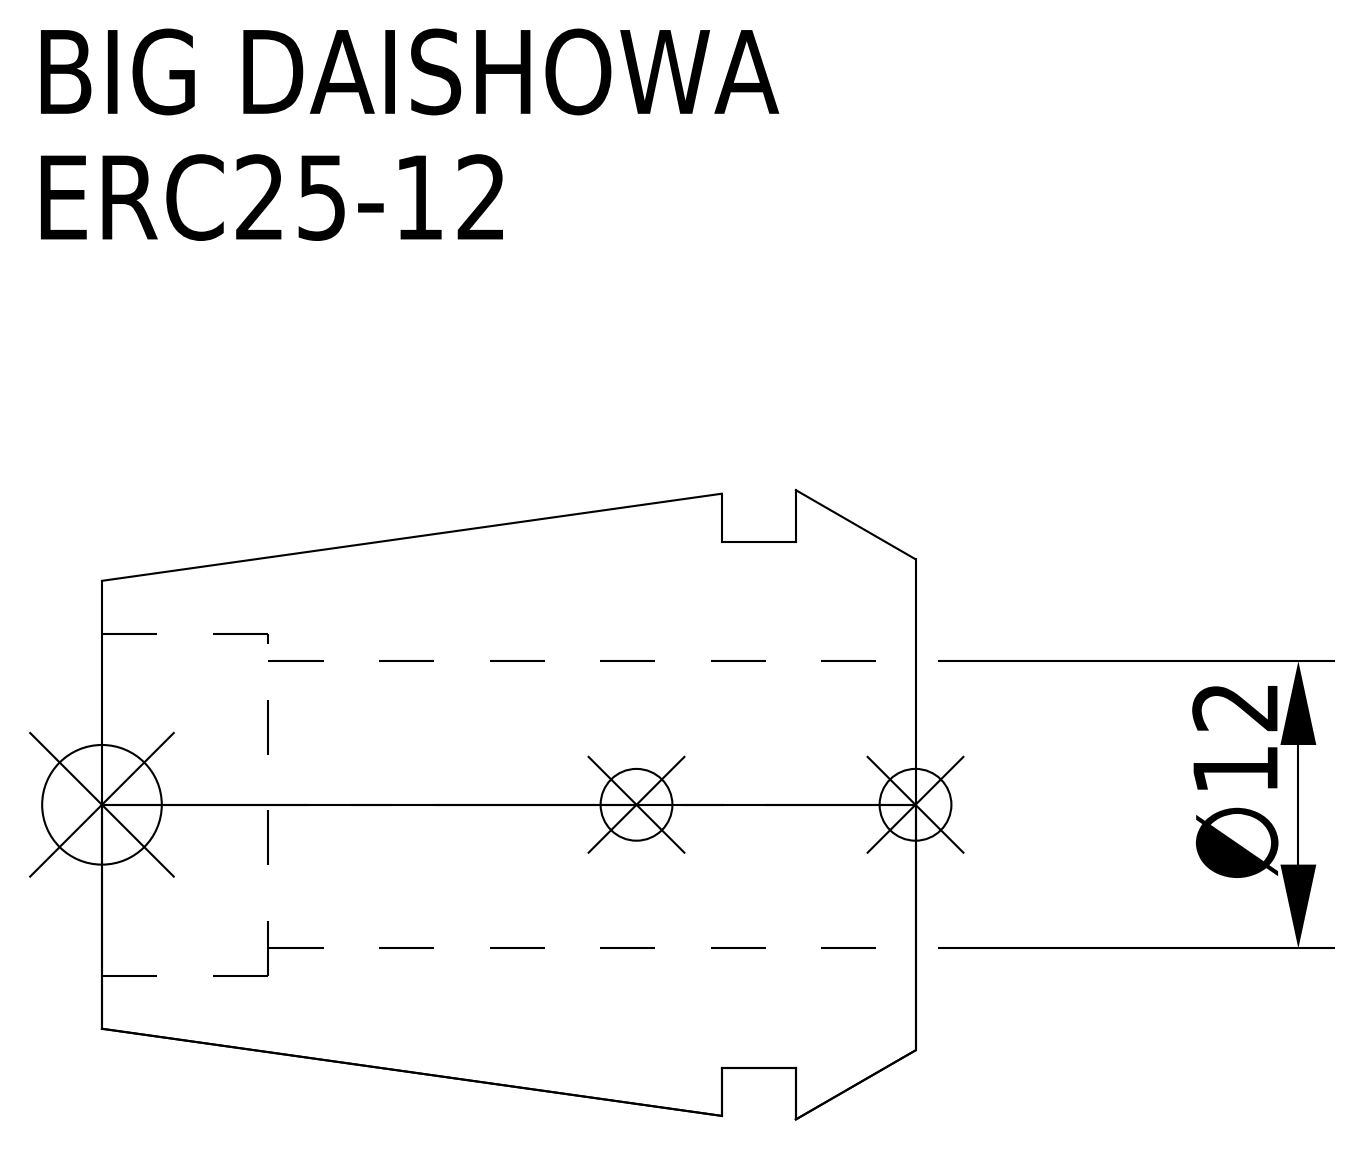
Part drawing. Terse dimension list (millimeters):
name: ERC25-12
written by: CREO PARAMETRIC BY PTC INC, 2016380 (AUTOMOTIVE_DESIGN)
unit: mm
bodies: 1 solid, 15 faces (5 planar, 6 cylindrical, 4 other)
size: 34 × 26.3 × 26.3
volume: 9 427 mm³; area: 4 502 mm²
holes: 1× ⌀12, 1× ⌀14.3
bosses: 1× ⌀22
face distances: 5, 8.1, 3.1, 34, 29, 25.9, 27.04, 22.04, 18.94, 6.96
